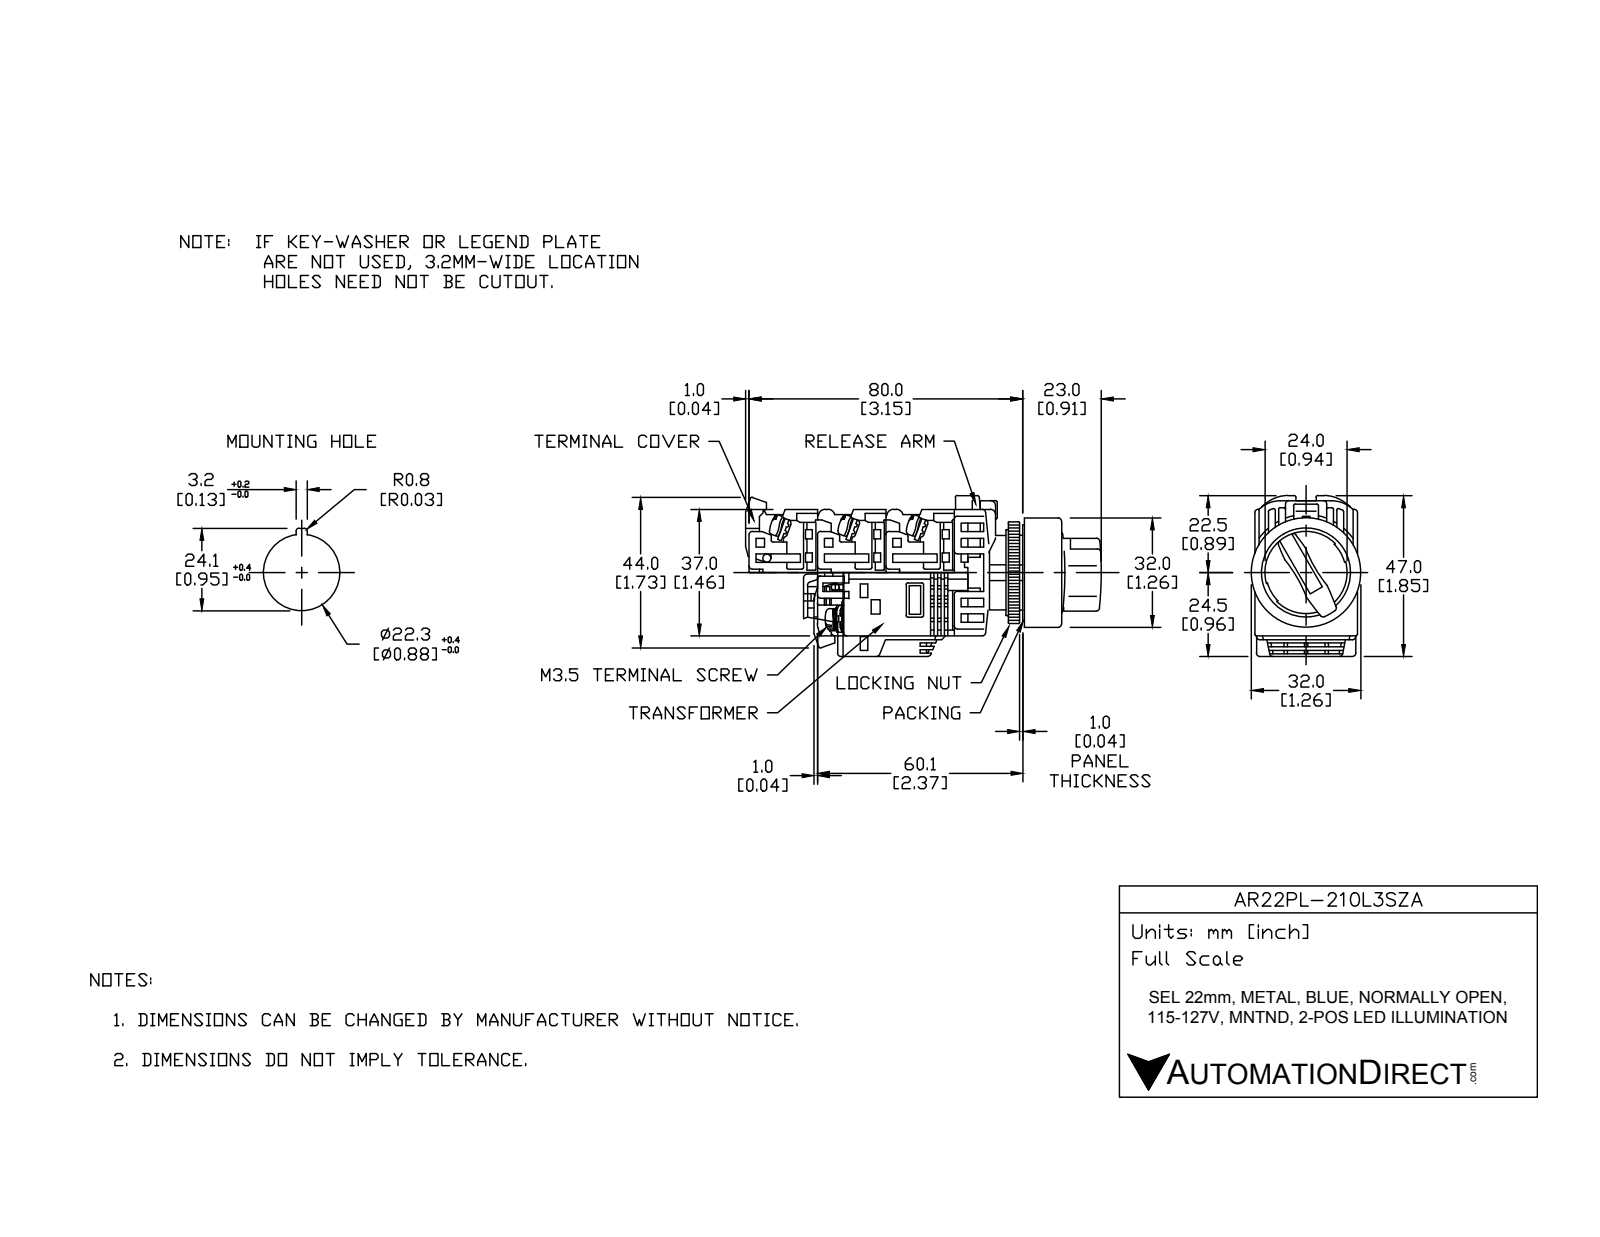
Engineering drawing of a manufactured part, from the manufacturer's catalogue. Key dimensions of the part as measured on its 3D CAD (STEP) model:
Part name (STEP PRODUCT): AR22PL-210L3SZA
STEP written by: SolidWorks 2017 (AUTOMOTIVE_DESIGN)
Units: millimetres
Bodies: 18 solids, 462 faces (317 planar, 118 cylindrical, 27 other)
Overall size (bounding box): 84.5 × 43.81 × 32
Volume: 48 971 mm³ · Surface area: 26 711 mm²
Round holes (diameter × count): ⌀21.8 ×1, ⌀22 ×1, ⌀25 ×1, ⌀31 ×1
Round bosses / shafts (diameter × count): ⌀5 ×4, ⌀32 ×1, ⌀30.5 ×1, ⌀29.8 ×1, ⌀24 ×1, ⌀21.75 ×1, ⌀17 ×1
Partial cylindrical surfaces — rounded edges, fillets, slot ends (radius × count): R0.5 ×39, R1.75 ×8, R1 ×6, R5 ×4, R4 ×2, R12 ×1, R16.59 ×1, R17.59 ×1
Main face-to-face distances: 1, 18, 29, 20, 3, 28.5, 0.5, 2, 21, 10
